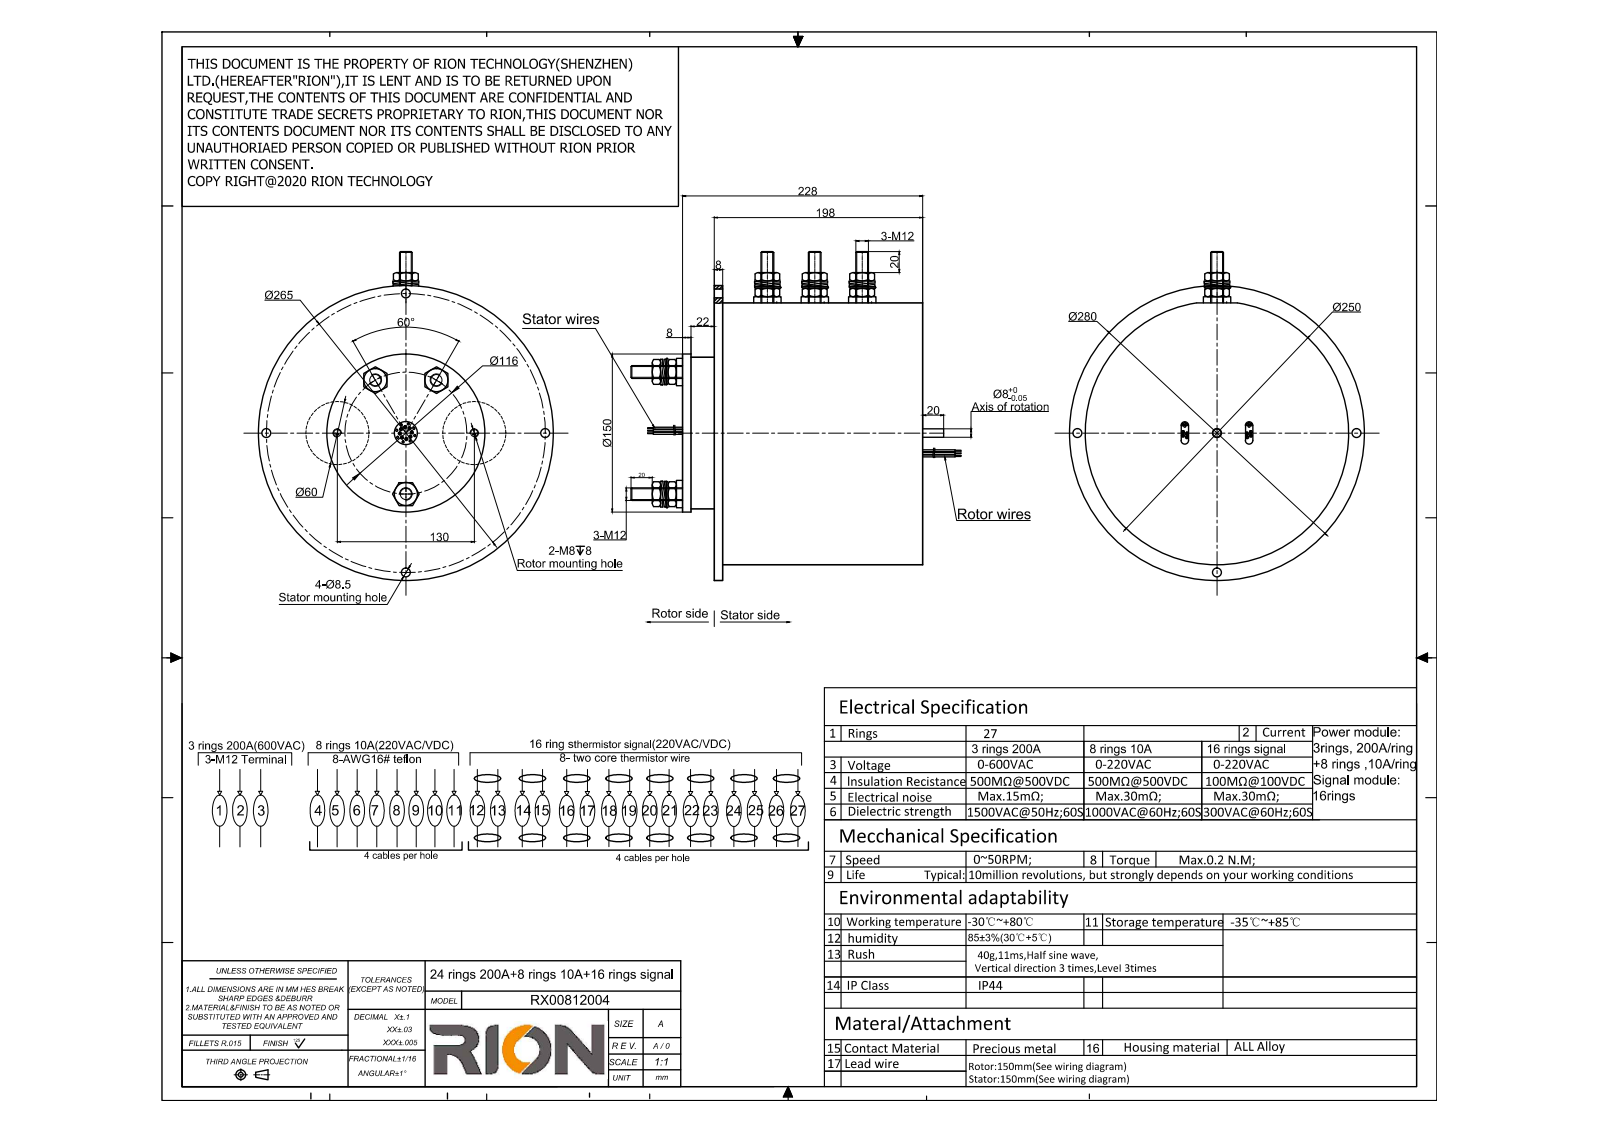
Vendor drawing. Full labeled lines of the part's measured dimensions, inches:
Part name (STEP PRODUCT): RX00812004--RZ250-R03200-P0810-S16
STEP written by: SolidWorks 2014 (CONFIG_CONTROL_DESIGN)
Units: inches
Bodies: 4 solids, 537 faces (195 planar, 323 cylindrical, 19 other)
Overall size (bounding box): 12.362 × 12.087 × 11.024
Volume: 635.3 in³ · Surface area: 511.5 in²
Round holes (diameter × count): ⌀0.335 ×4, ⌀0.276 ×2, ⌀0.866 ×1
Round bosses / shafts (diameter × count): ⌀0.098 ×16, ⌀0.083 ×16, ⌀1.024 ×6, ⌀0.787 ×6, ⌀0.472 ×6, ⌀11.024 ×1, ⌀9.843 ×1, ⌀5.906 ×1
Partial cylindrical surfaces — rounded edges, fillets, slot ends (radius × count): R0.138 ×4
Main face-to-face distances: 7.795, 1.181, 8.976, 0.315, 1.496, 7.48, 0.866, 1.142, 1.534, 8.661
Hole centre spacings: 5.217, 5.81, 7.377, 2.559, 2.657, 7.776, 10.433, 5.118
